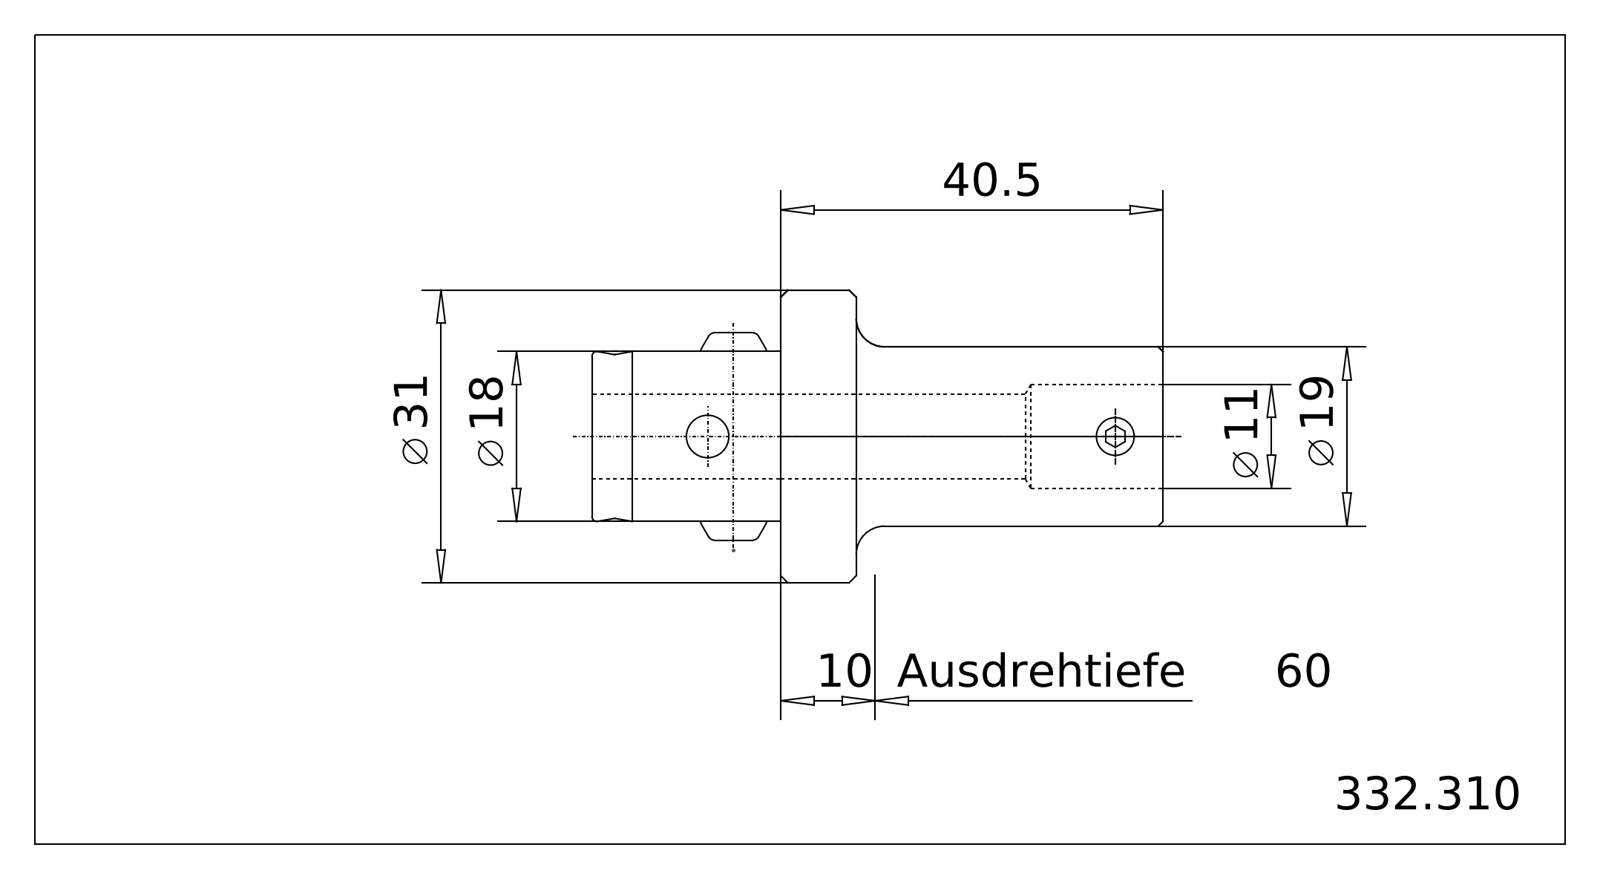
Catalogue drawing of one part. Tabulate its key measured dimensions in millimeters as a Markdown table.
| quantity | value |
| --- | --- |
| part name | 332.310 Kaiser CK3 X CK1 X 60\|690.431 Kaiser ETL M4 X 5 CK1_Standard;NONE; 332.310 Kaiser CK3 X CK1 X 60\|332.310 Kaiser CK3 X CK1 X 60_Standard;NONE; 332.310 Kaiser CK3 X CK1 X 60\|691.503 Kaiser ETL �7 X 22K_Standard\|692.272 O-Ring_Standard;NONE; 332.310 Kaiser CK3 X CK1 X 60\|691.503 Kaiser ETL �7 X 22K_Standard\|691.523 Mitnehmerbolzen_Standard;NONE |
| STEP written by | ACIS (automotive_design) |
| units | millimeters |
| bodies | 4 solids, 138 faces (35 planar, 34 cylindrical, 69 other) |
| overall size | 60.5 × 31 × 31 |
| volume | 16 463 mm³ |
| surface area | 7 719 mm² |
| round holes (diameter × count) | 3.2 × 1, 4.2 × 1, 4.5 × 1, 7 × 1, 9 × 1, 11 × 1, 11.5 × 1 |
| round bosses / shafts (diameter × count) | 4 × 2, 31 × 1, 19 × 1, 18 × 1, 6.93 × 1 |
| partial cylindrical surfaces (radius × count) | 1.5 × 2 |
| main face-to-face distances | 8.37, 28.37, 20, 32.13, 40.5, 60.5, 40.38, 8.25, 20.12, 9.38 |
| hole center spacings | 43.2 |
